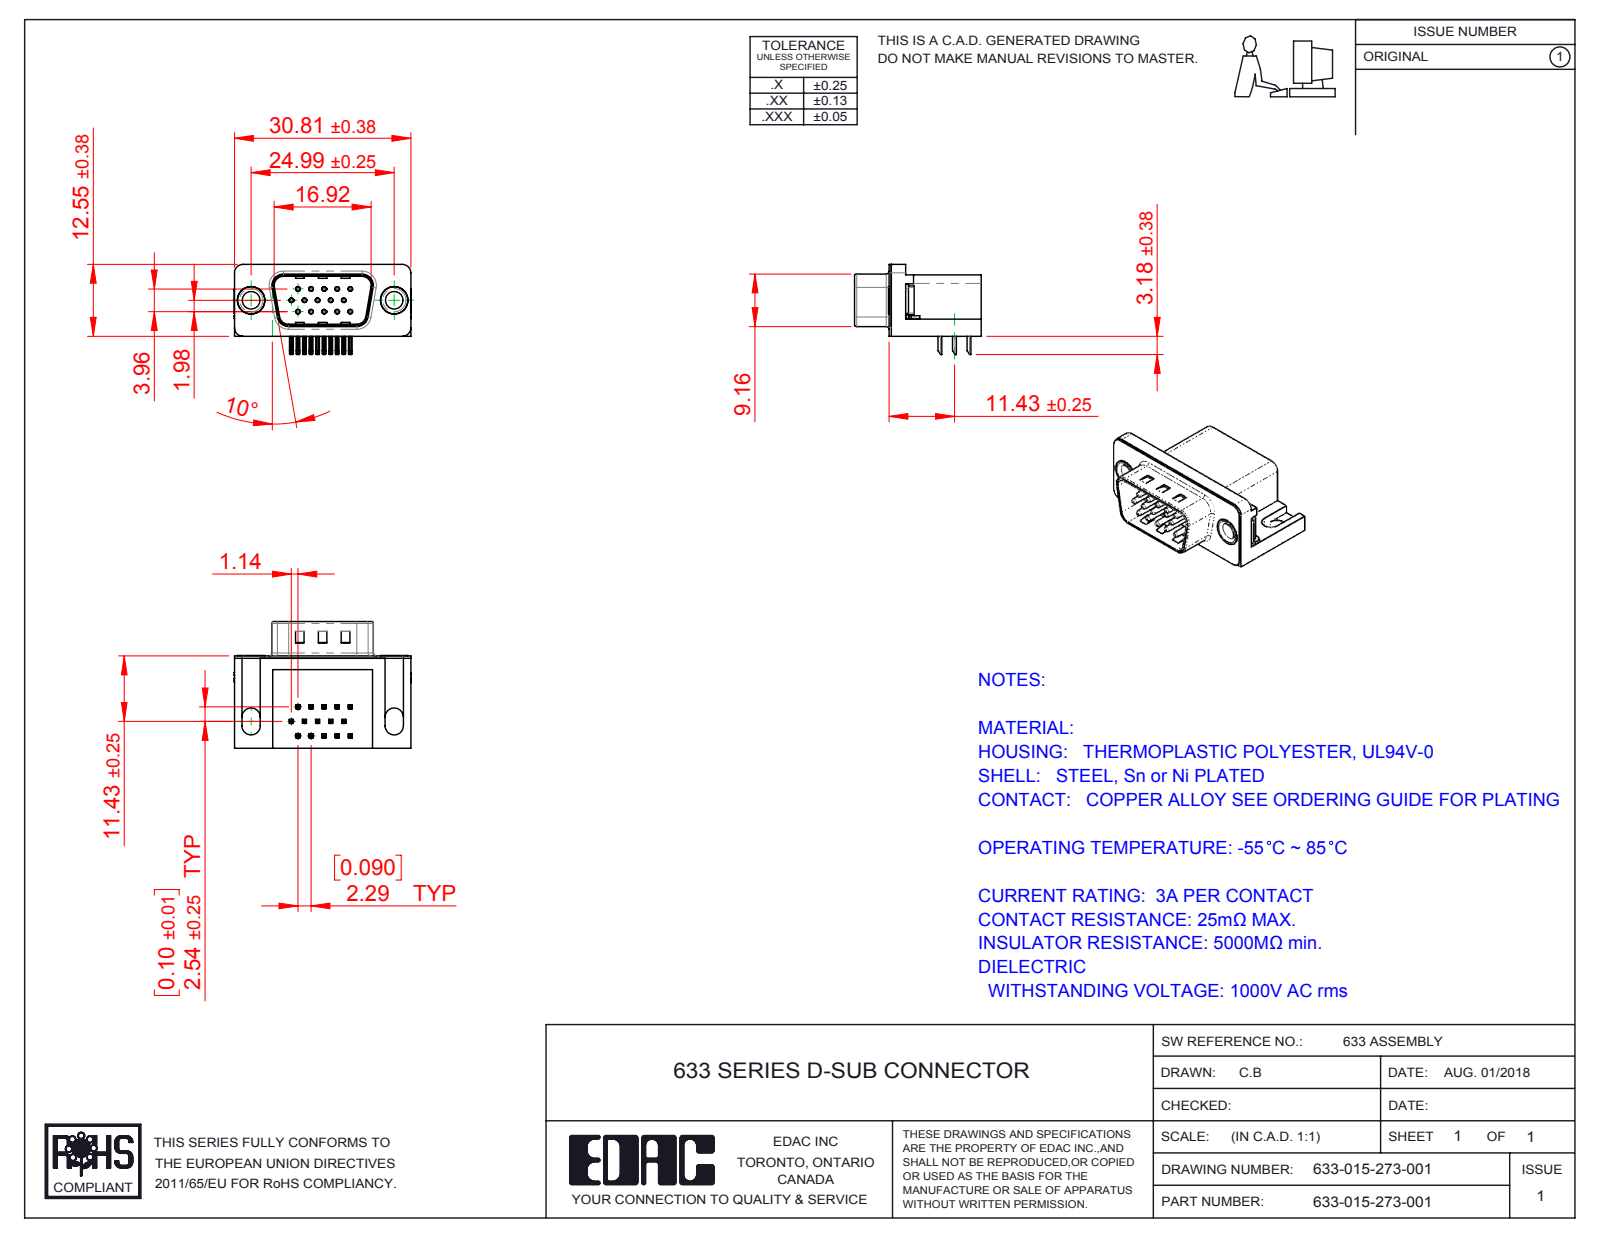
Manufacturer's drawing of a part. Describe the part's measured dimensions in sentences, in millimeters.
The part is named "633 Non Board Mount; 633 Contact Top; 633 Contact Middle; 633 Contact Middle_Recessed (+5 more)". Its 3-D file was written by "SolidWorks 2016 (CONFIG_CONTROL_DESIGN)". It is 21 solids with 1399 faces: 861 planar, 421 cylindrical and 117 other. Overall it measures 30.89 by 22.1 by 15.73 millimeters. Its volume is 4 014 cubic millimeters and its surface area 5 179 square millimeters. Round holes: 15 of diameter 0.35, 15 of diameter 0.8, 2 of diameter 3.05, 2 of diameter 4, 2 of diameter 4.8, 2 of diameter 5. Round bosses or shafts: 15 of diameter 0.75, 2 of diameter 4.9, 2 of diameter 4.75, 2 of diameter 3.85. Partial cylindrical surfaces (rounded edges, fillets, slot ends): 68 of radius 0.25, 30 of radius 0.12, 16 of radius 1, 9 of radius 0.5, 8 of radius 1.6, 7 of radius 1.5, 4 of radius 0.9, 4 of radius 2. The main face-to-face distances are 0.4, 10.35, 15.7, 2.9, 2.5, 6.7, 16.1, 0.35, 10.7, 13.2. The hole center spacings are 3.96, 2.28, 4.57, 2.29, 6.05, 6.86, 7.92, 6.04.
